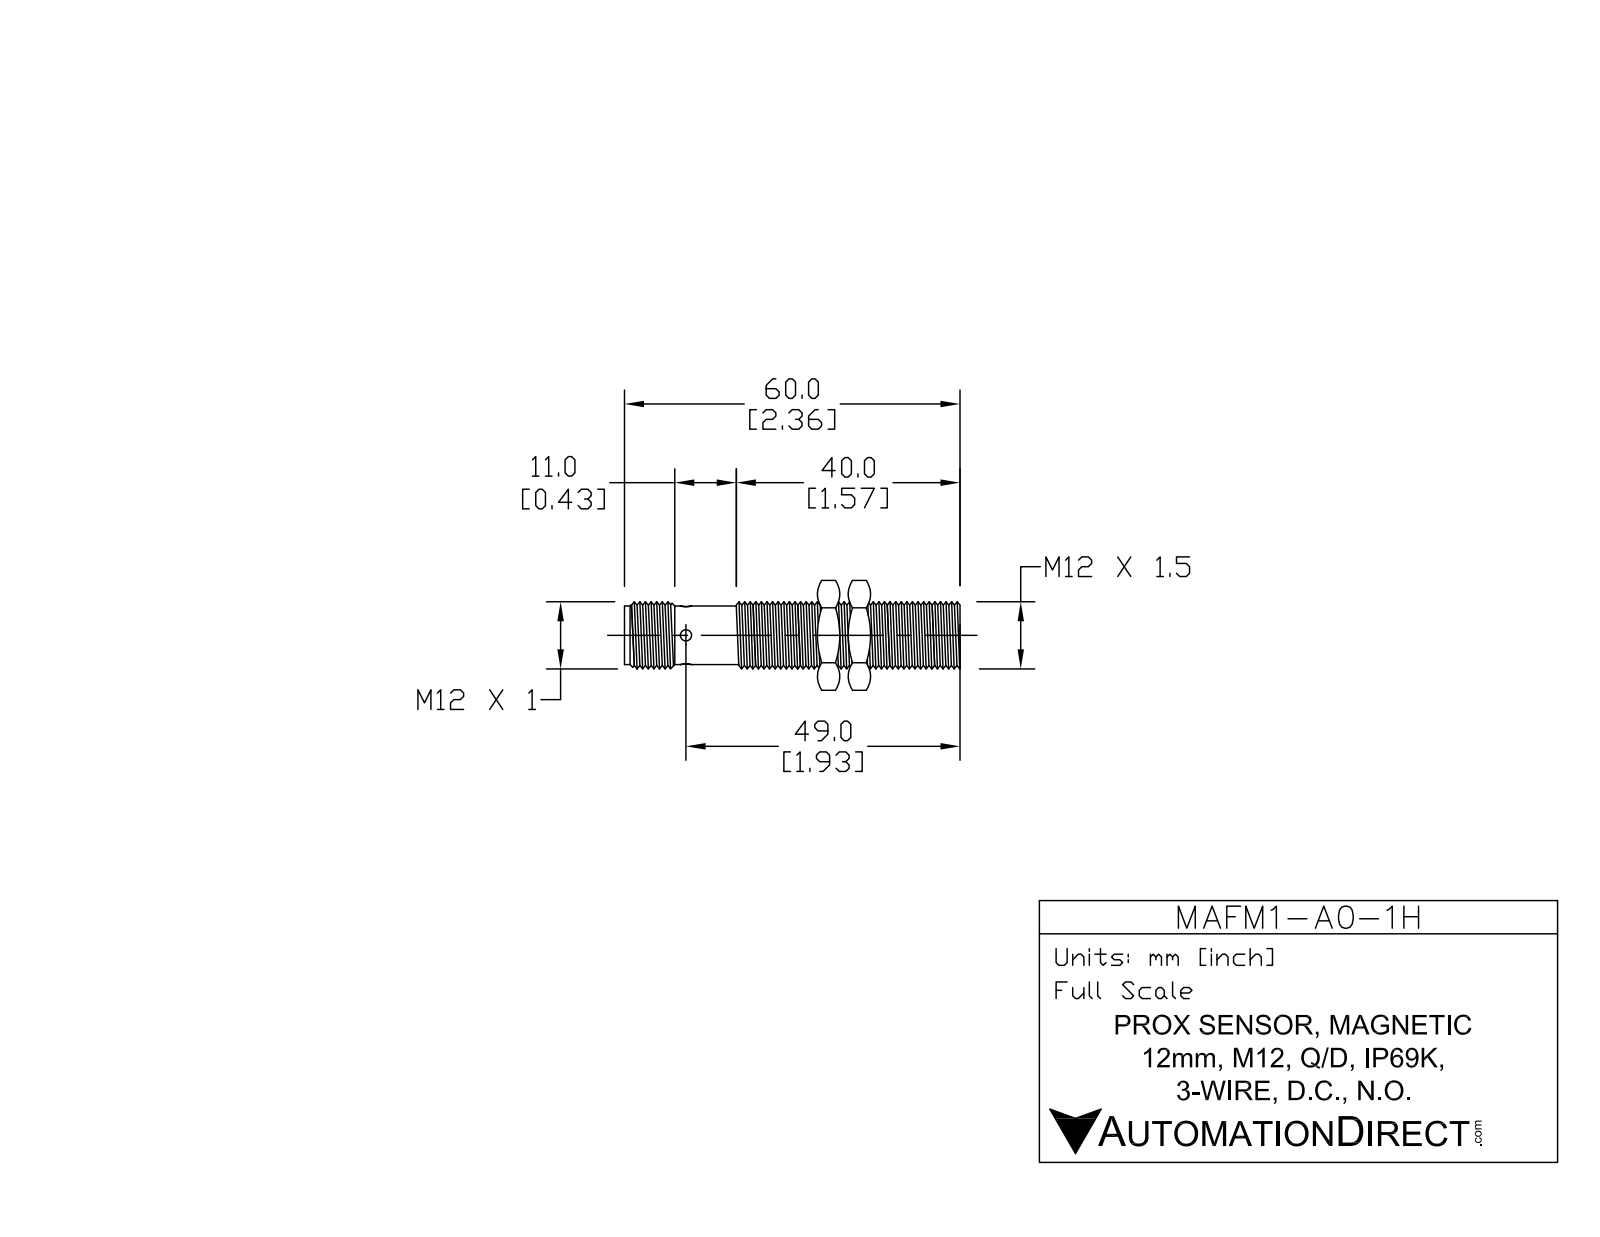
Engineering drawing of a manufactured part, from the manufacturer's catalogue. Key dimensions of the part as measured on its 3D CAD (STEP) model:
Part name (STEP PRODUCT): MAFM1-A0-1H
STEP written by: SolidWorks 2017 (AUTOMOTIVE_DESIGN)
Units: inches
Bodies: 3 solids, 100 faces (26 planar, 32 cylindrical, 42 other)
Overall size (bounding box): 2.362 × 0.773 × 0.669
Volume: 0.436 in³ · Surface area: 6.196 in²
Round holes (diameter × count): ⌀0.098 ×2, ⌀0.331 ×1, ⌀0.43 ×1
Round bosses / shafts (diameter × count): ⌀0.472 ×1, ⌀0.417 ×1, ⌀0.413 ×1, ⌀0.406 ×1
Partial cylindrical surfaces — rounded edges, fillets, slot ends (radius × count): R0.024 ×1, R0.177 ×1
Main face-to-face distances: 0.157, 0.669, 0.315, 0.787, 0.63, 0.945, 1.067, 1.224, 1.382, 2.012
